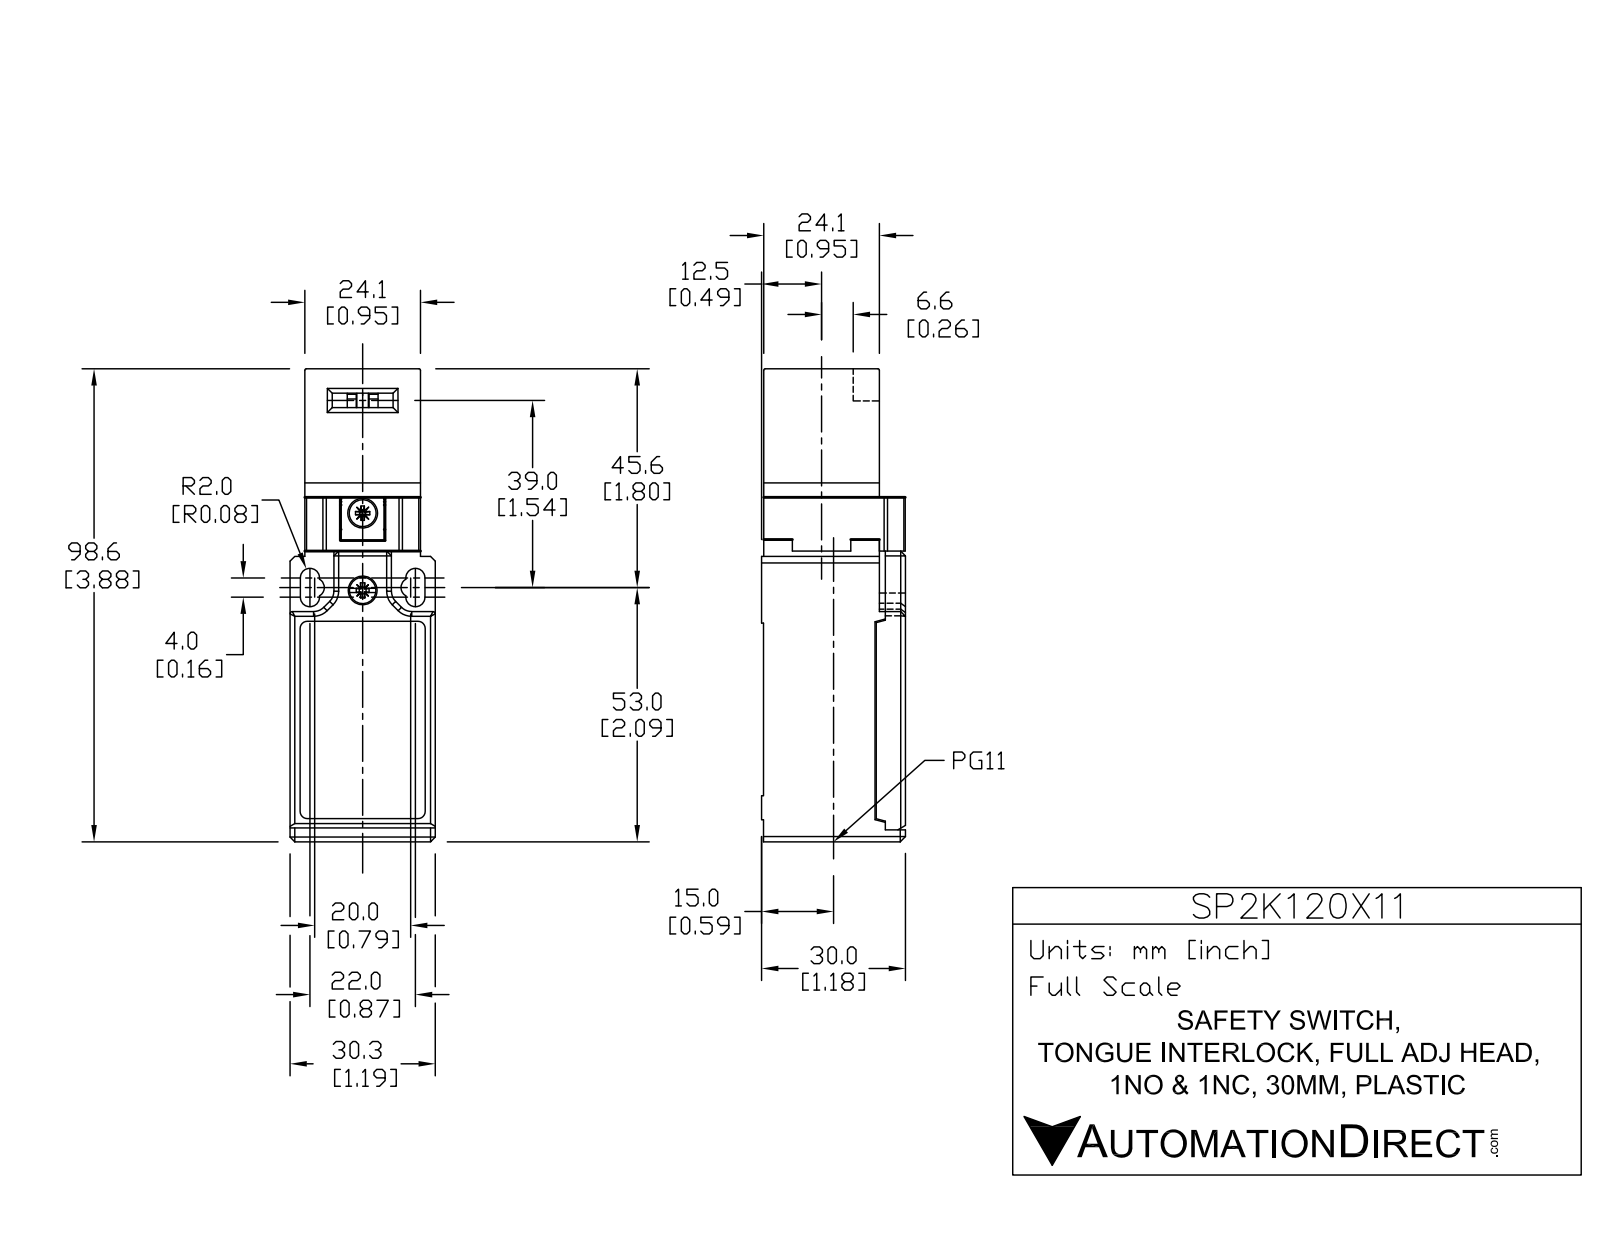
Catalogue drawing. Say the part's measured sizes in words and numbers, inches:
The part is named "SP2K120X11". Its 3-D file was written by "SolidWorks 2017 (AUTOMOTIVE_DESIGN)". It is 3 solids with 160 faces: 111 planar, 36 cylindrical and 13 other. Overall it measures 3.902 by 1.204 by 1.193 inches. Its volume is 4.393 cubic inches and its surface area 28.76 square inches. Round holes: 1 of diameter 0.236, 1 of diameter 0.591, 1 of diameter 0.669, 1 of diameter 0.748. Round bosses or shafts: 1 of diameter 0.22. Partial cylindrical surfaces (rounded edges, fillets, slot ends): 6 of radius 0.079, 4 of radius 0.02, 4 of radius 0.118, 1 of radius 0.394, 1 of radius 0.4. The main face-to-face distances are 0.124, 1.069, 0.945, 1.193, 1.165, 0.441, 0.22, 1.181, 2.406, 2.846. The hole center spacings are 0.083.
